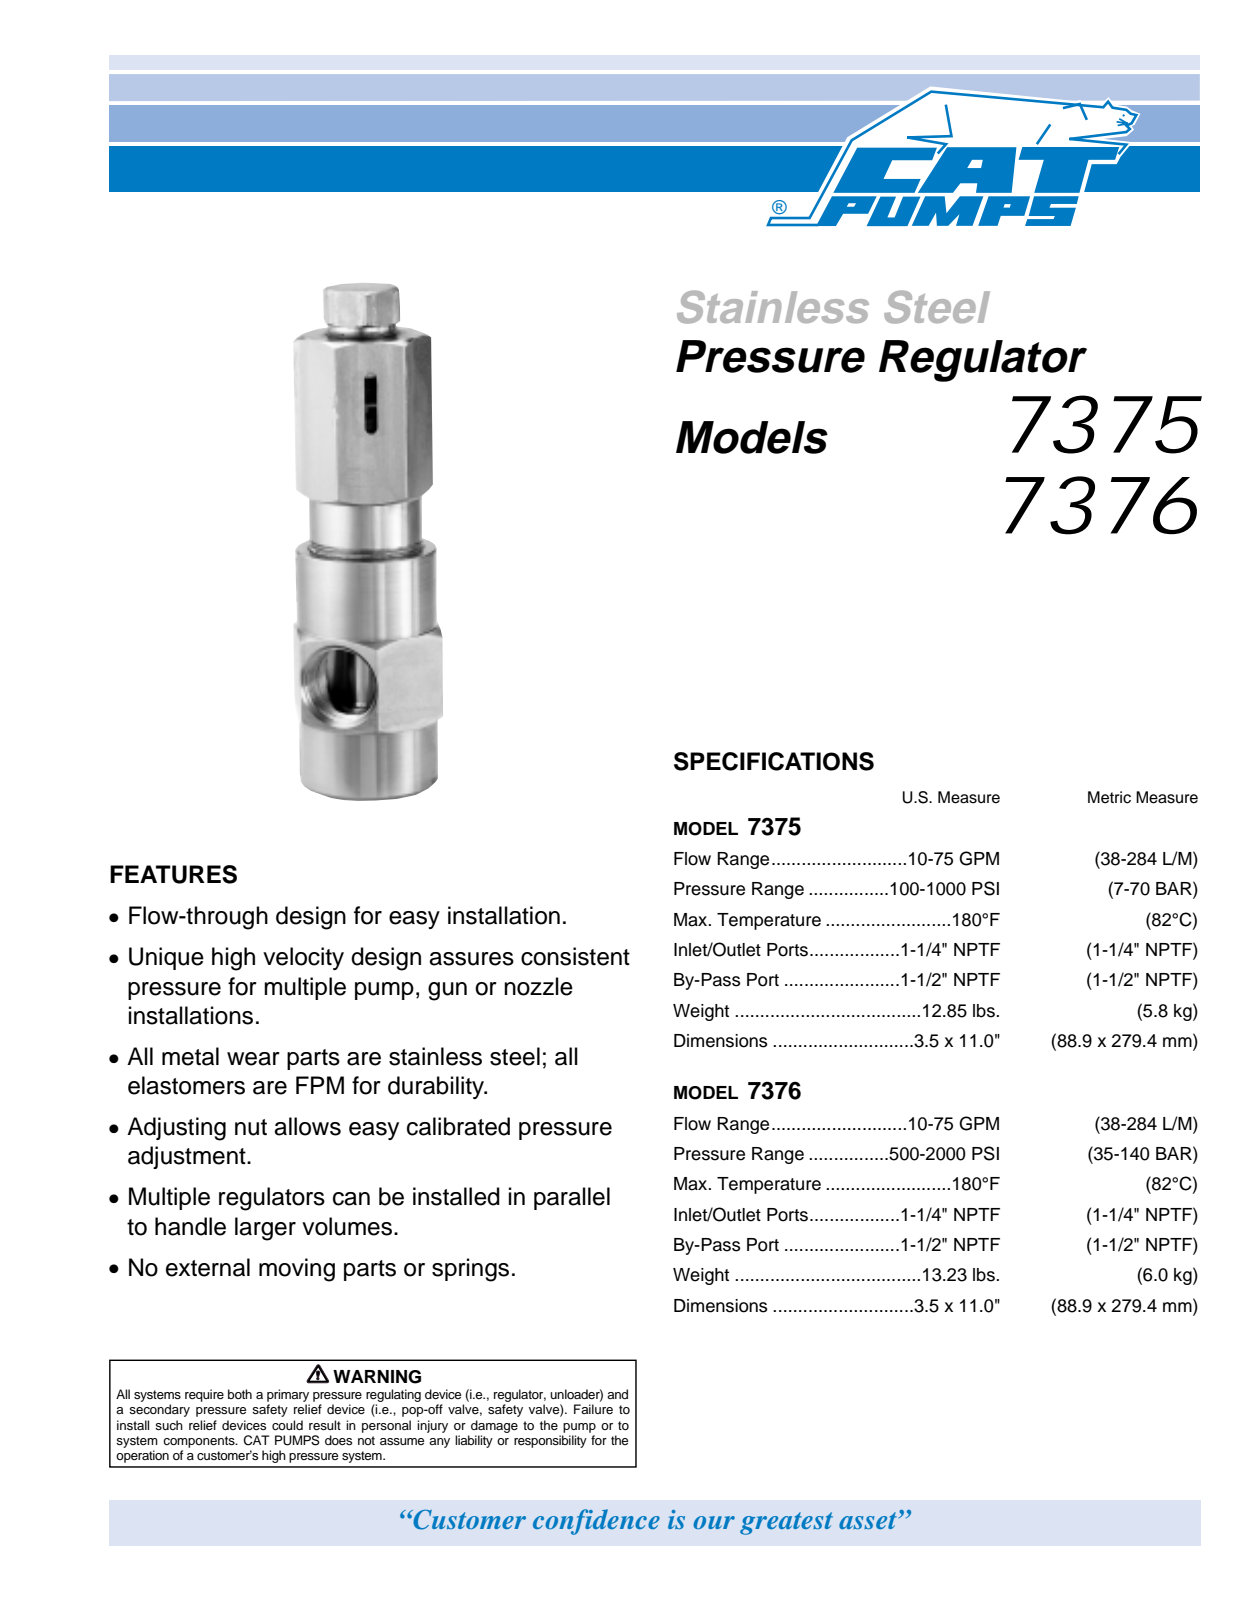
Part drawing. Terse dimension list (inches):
name: 30716; 30706; 30666; 7375
written by: SolidWorks 2009 (AUTOMOTIVE_DESIGN)
unit: in
bodies: 3 solids, 157 faces (41 planar, 38 cylindrical, 78 other)
size: 11.111 × 3.464 × 3
volume: 32.95 in³; area: 194.5 in²
holes: 1× ⌀1.047, 1× ⌀1.123, 1× ⌀1.41, 1× ⌀1.719, 1× ⌀1.75, 1× ⌀2, 1× ⌀2.063, 1× ⌀2.25, 1× ⌀2.285, 1× ⌀2.4
bosses: 1× ⌀2.95, 1× ⌀2.373, 1× ⌀1.5, 1× ⌀1.44
rounds: 4× R0.125, 1× R0.742
face distances: 3, 2.5, 2.499, 2.501, 9.61, 4.461, 5.15, 0.75, 3.711, 8.86
